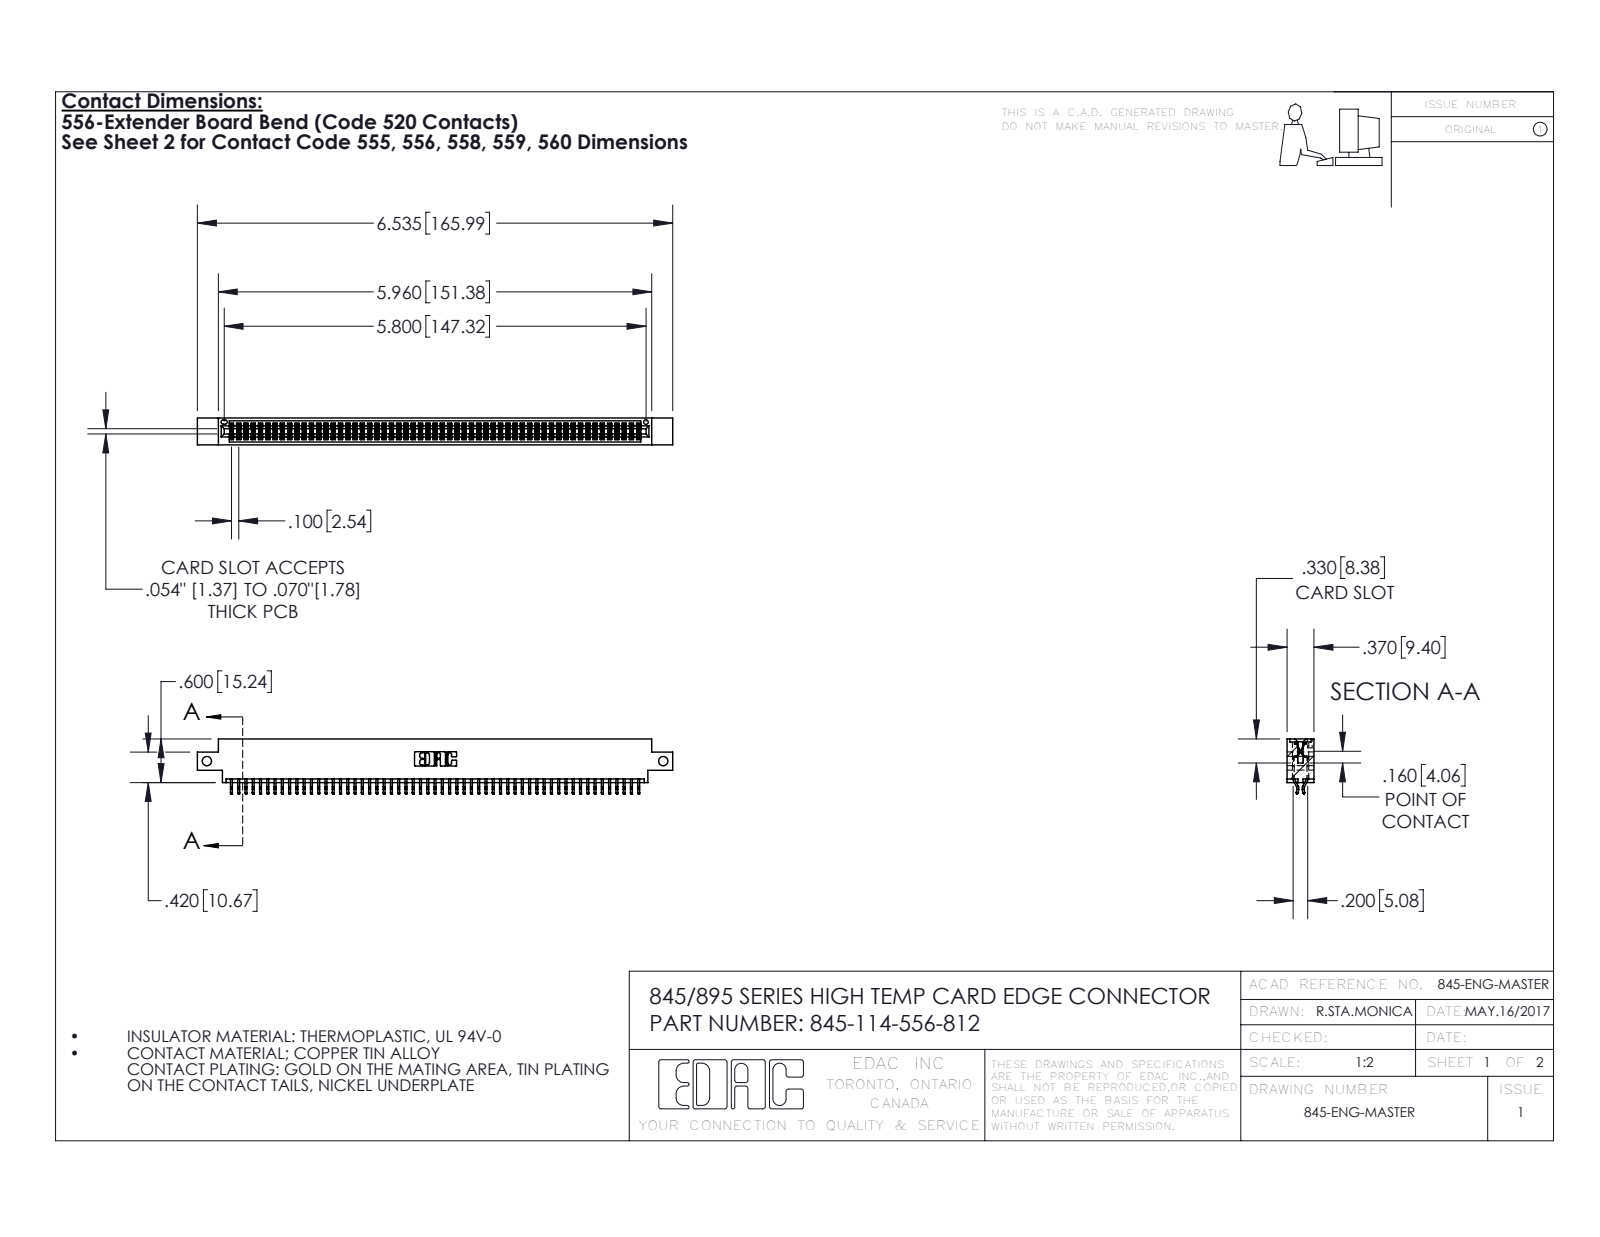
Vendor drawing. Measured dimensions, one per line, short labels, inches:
name: 345-114-556-812; 345-292-001_556 Tail; 345 Part_0.170 Offset - Side Mount
written by: SolidWorks 2016 (CONFIG_CONTROL_DESIGN)
unit: in
bodies: 115 solids, 6514 faces (4302 planar, 2212 cylindrical, 0 other)
size: 6.535 × 0.757 × 0.37
volume: 0.98 in³; area: 37.1 in²
holes: 2× ⌀0.128, 1× ⌀0.064
rounds: 171× R0.006, 22× R0.01, 6× R0.007, 6× R0.031, 3× R0.026, 2× R0.01, 2× R0.014, 2× R0.019
face distances: 0.298, 0.072, 0.37, 0.025, 0.2, 0.098, 0.272, 0.225, 0.175, 0.149
hole spacings: 6.275
